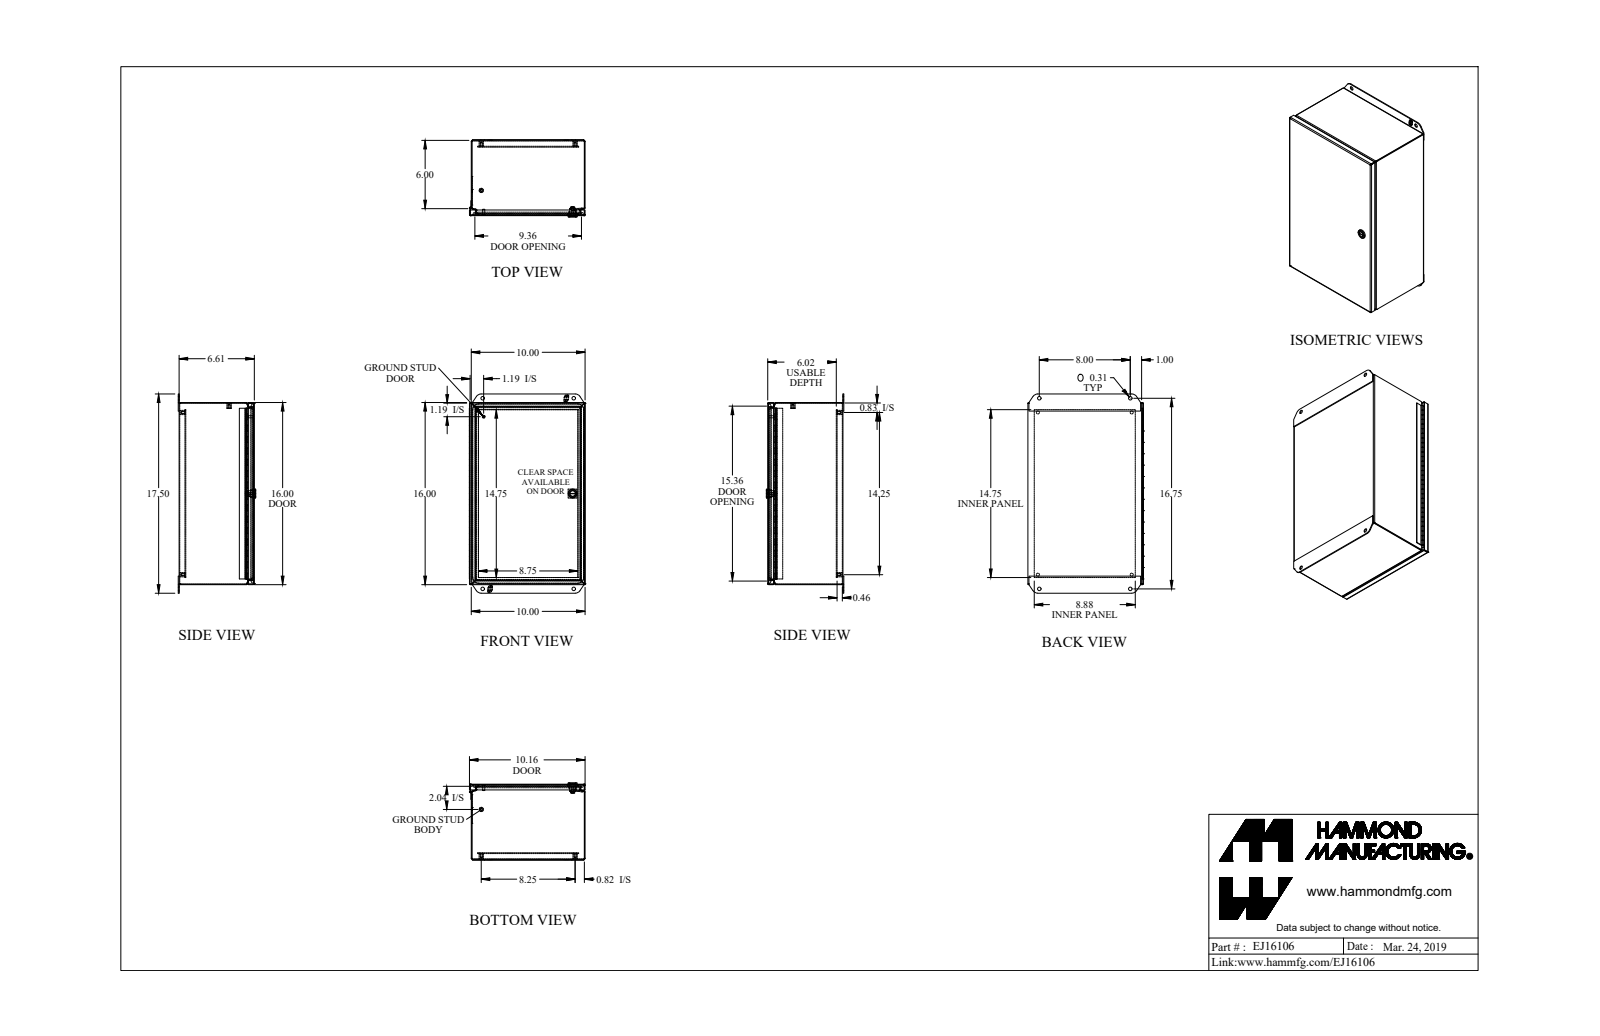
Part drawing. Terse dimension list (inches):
name: EJ16106_Default
written by: SolidWorks 2019 (CONFIG_CONTROL_DESIGN)
unit: in
bodies: 16 solids, 771 faces (425 planar, 254 cylindrical, 92 other)
size: 17.5 × 10.165 × 6.805
volume: 56.45 in³; area: 1 870 in²
holes: 5× ⌀0.156, 4× ⌀0.265, 4× ⌀0.313, 1× ⌀0.05, 1× ⌀0.516
bosses: 5× ⌀0.375, 1× ⌀0.788, 1× ⌀0.535, 1× ⌀0.496, 1× ⌀0.435, 1× ⌀0.25, 1× ⌀0.188, 1× ⌀0.1
rounds: 16× R0.029, 16× R0.086, 10× R0.281, 4× R0.25, 4× R0.499, 4× R0.5, 2× R0.06, 2× R0.539
face distances: 0.057, 6.554, 9.943, 0.072, 0.589, 6.611, 6.497, 0.46, 0.517, 6.094
hole spacings: 1.257, 15.5, 17.5, 14.25, 8.22, 16.465, 7.128, 8
